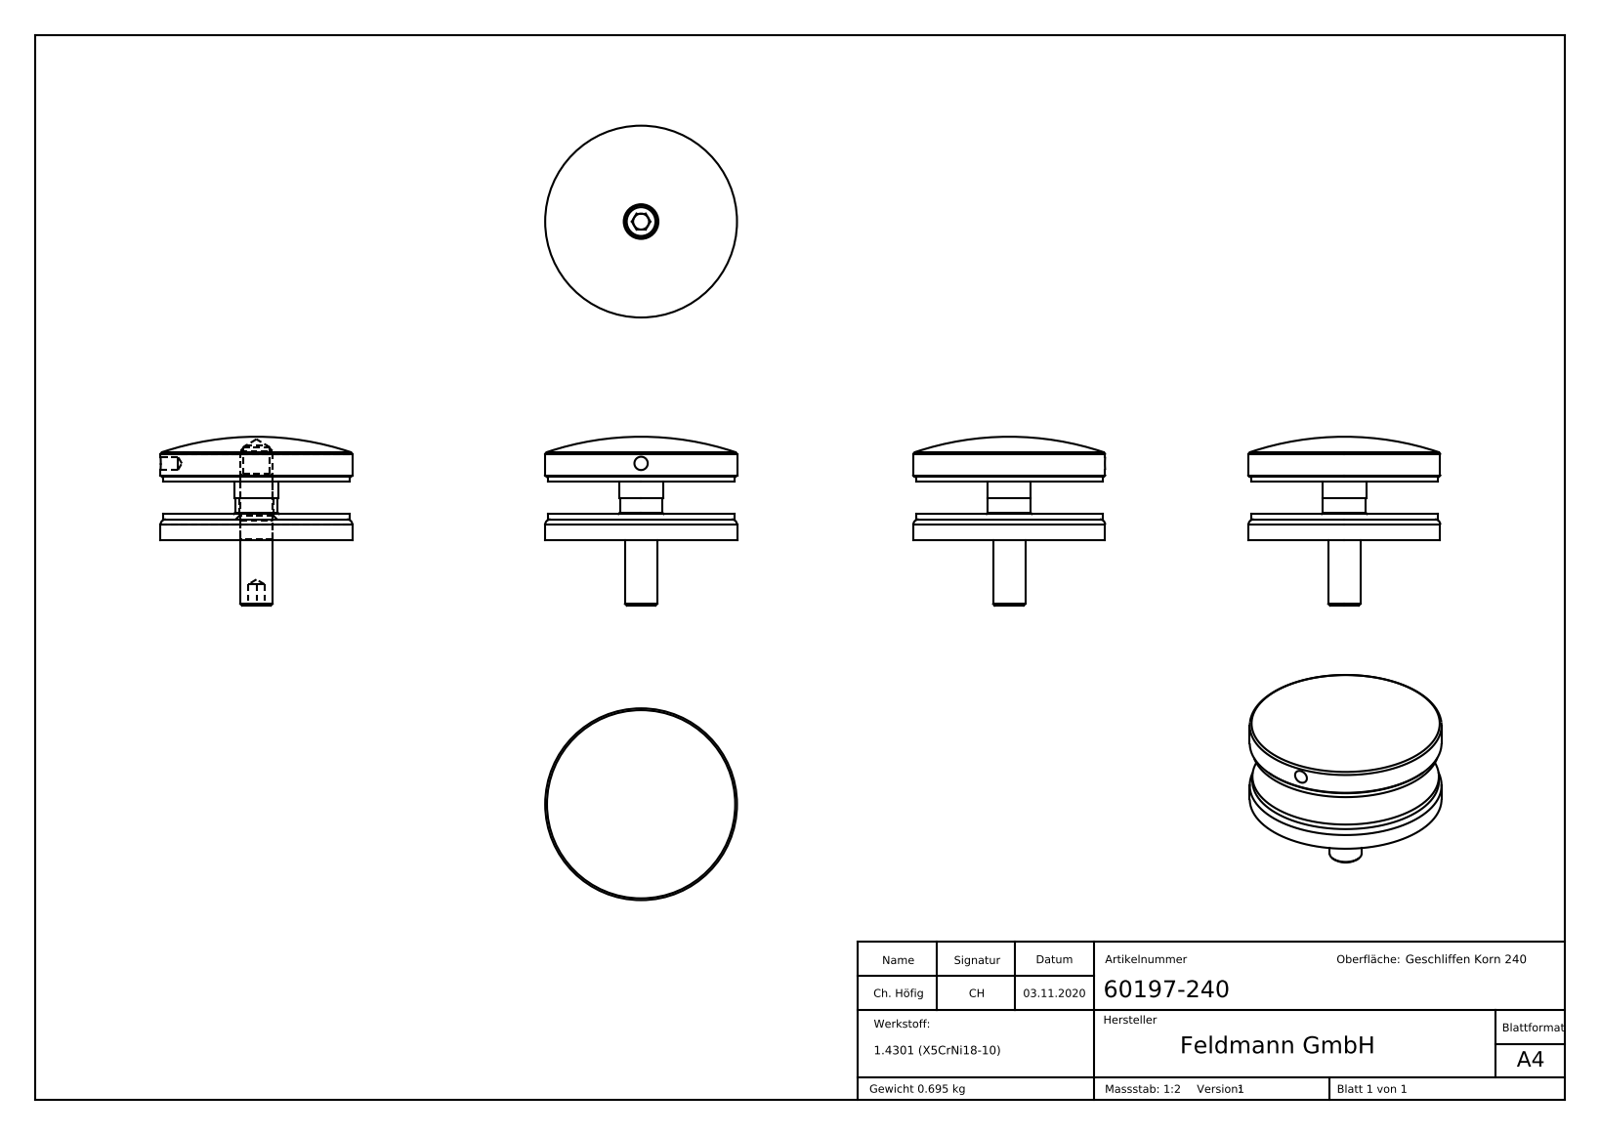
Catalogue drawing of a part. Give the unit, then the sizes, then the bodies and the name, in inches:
Units: inches
Overall size (bounding box): 2.835 × 2.835 × 2.574
Round holes (diameter × count): ⌀0.197 ×1, ⌀0.402 ×1, ⌀0.472 ×1, ⌀0.492 ×1
Round bosses / shafts (diameter × count): ⌀2.835 ×1, ⌀2.756 ×1, ⌀0.642 ×1, ⌀0.63 ×1
Main face-to-face distances: 0.079, 0.551, 0.63, 0.315, 0.945, 0.866, 0.394, 0.472, 0.236, 0.96
Volume: 6.202 in³ · Surface area: 62.34 in²
Bodies: 6 solids, 288 faces (144 planar, 26 cylindrical, 118 other)
Part name (STEP PRODUCT): 60197-XXX Teil3; 60197-XXX Teil1_60197-240 Teil1; 60197-XXX Teil5; 60197-240 (+8 more)
STEP written by: SolidWorks 2018 (CONFIG_CONTROL_DESIGN)
